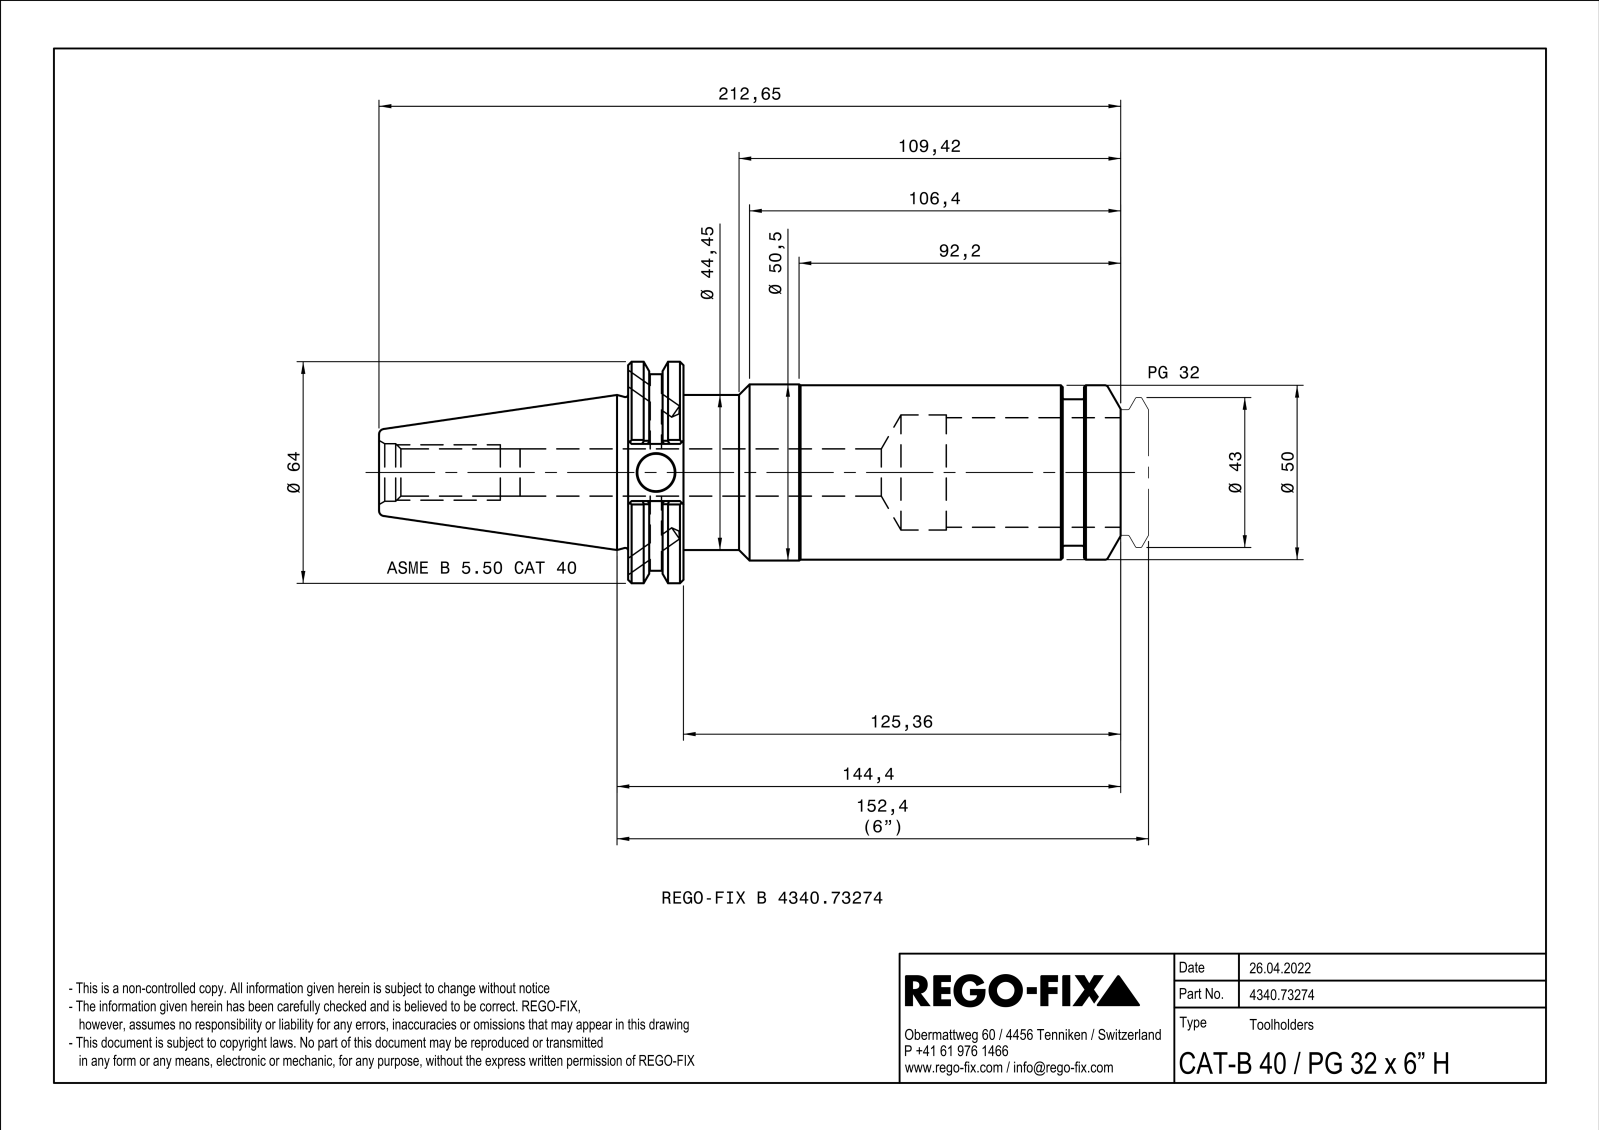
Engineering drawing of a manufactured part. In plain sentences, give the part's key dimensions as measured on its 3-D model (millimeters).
The part is named "NOCUT". Its 3-D file was written by "SIEMENS PLM Software Solid Edge ST10 (AUTOMOTIVE_DESIGN)". It is 1 solid with 102 faces: 33 planar, 22 cylindrical and 47 other. Overall it measures 212.65 by 63.5 by 60.79 millimeters. Its volume is 272 533 cubic millimeters and its surface area 49 540 square millimeters. Round holes: 1 of diameter 10.7, 1 of diameter 13.53, 1 of diameter 16.5, 1 of diameter 33. Round bosses or shafts: 1 of diameter 63.5, 1 of diameter 56.36, 1 of diameter 50.5, 1 of diameter 50, 1 of diameter 44.45, 1 of diameter 42. Partial cylindrical surfaces (rounded edges, fillets, slot ends): 4 of radius 0.5. The main face-to-face distances are 15.87, 108.76, 124.63, 6.1, 114.86, 130.73, 10.5, 16.6, 125.36, 141.23.
